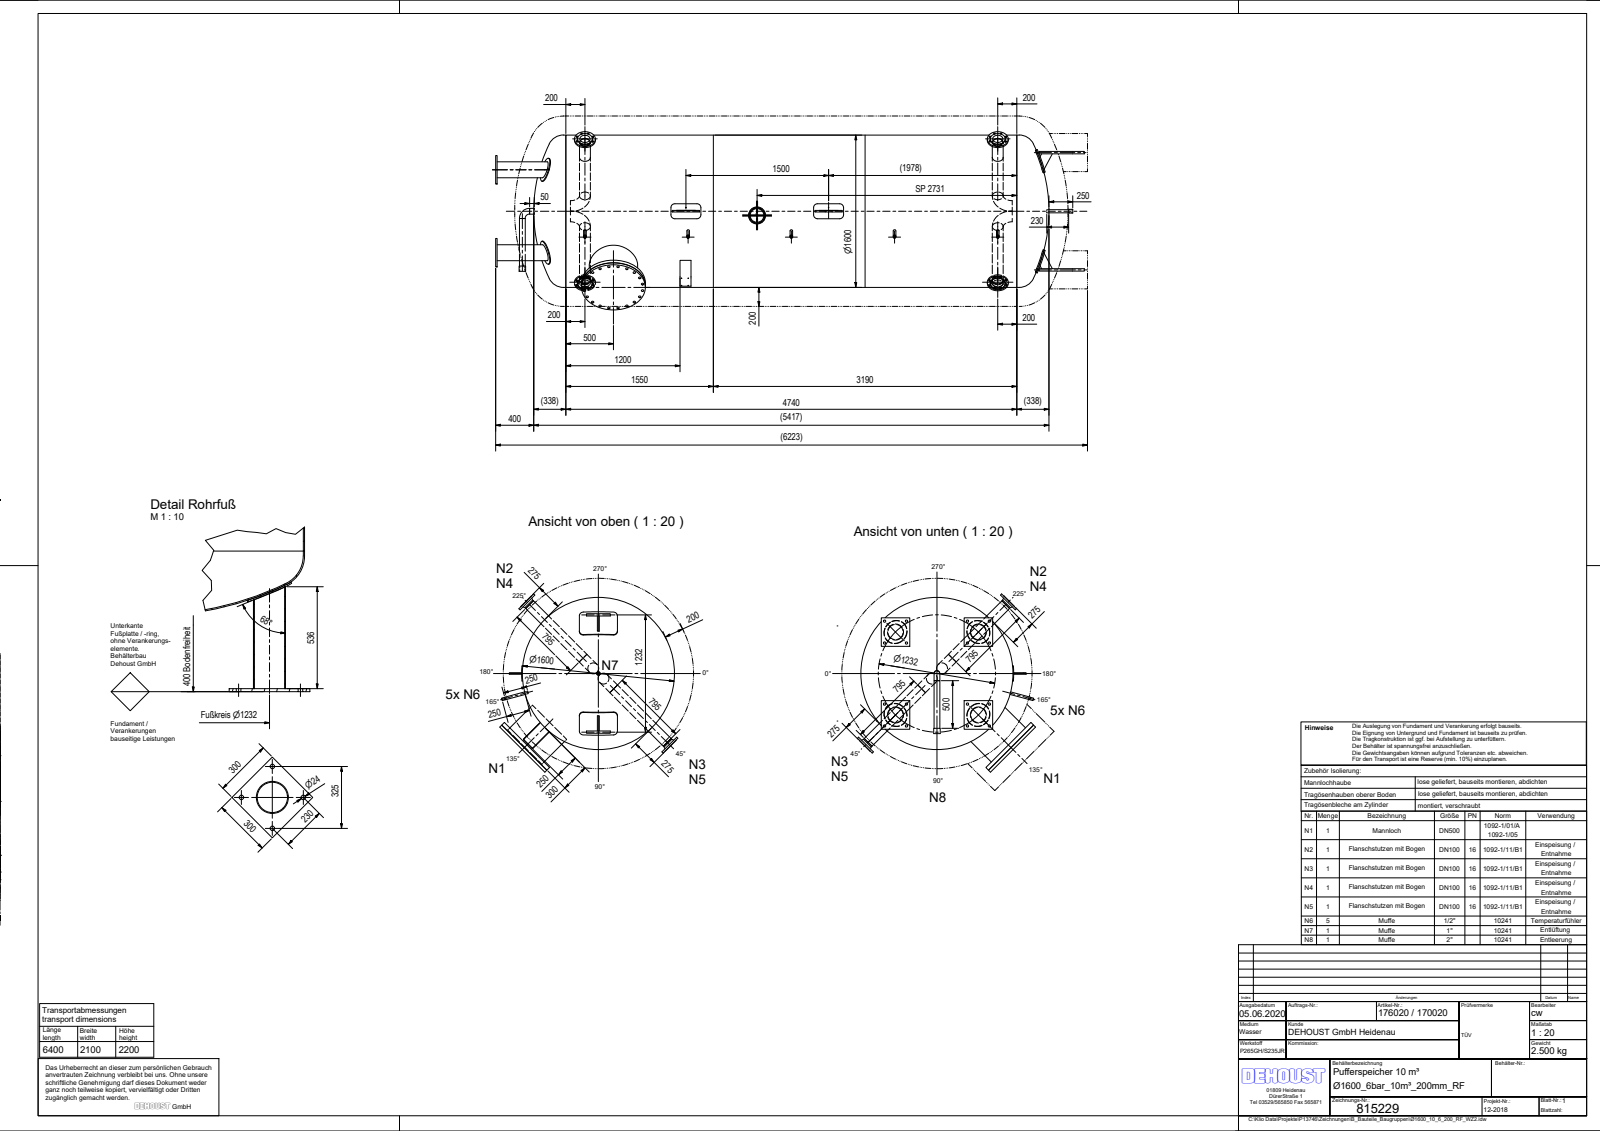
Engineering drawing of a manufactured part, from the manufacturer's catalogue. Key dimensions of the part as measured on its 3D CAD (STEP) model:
Part name (STEP PRODUCT): Ø1600_10_6_200_RF_WZ2; Klöpper_Gew_Ø1600_6,4; Zyl_Ø1600_6x1550-5x3190; TÖB_Puffer_Ø1600_6, 4_200 (+8 more)
STEP written by: Autodesk Inventor 2019 (AUTOMOTIVE_DESIGN)
Units: millimetres
Bodies: 58 solids, 451 faces (179 planar, 226 cylindrical, 46 other)
Overall size (bounding box): 6188.64 × 1872.42 × 1872.42
Volume: 277 900 000 mm³ · Surface area: 69 950 000 mm²
Round holes (diameter × count): ⌀26 ×40, ⌀18 ×32, ⌀24 ×16, ⌀18.63 ×5, ⌀21.7 ×5, ⌀26.9 ×5, ⌀5.8 ×4, ⌀106.3 ×4, ⌀107.1 ×4, ⌀159.3 ×4, ⌀5 ×2, ⌀52.3 ×2
Round bosses / shafts (diameter × count): ⌀114.3 ×8, ⌀26.9 ×5, ⌀26.4 ×5, ⌀250 ×4, ⌀220 ×4, ⌀168.3 ×4, ⌀158 ×4, ⌀670 ×2
Partial cylindrical surfaces — rounded edges, fillets, slot ends (radius × count): R42 ×16, R10 ×6, R6 ×4, R5 ×2, R36 ×2, R72 ×2, R125 ×1, R807 ×1
Main face-to-face distances: 16, 2972.69, 3167.69, 195, 2988.69, 3183.69, 28, 600, 303.5, 903.5
Hole centre spacings: 90, 310, 191.59, 1085, 4340, 501.59, 2170, 127.28
